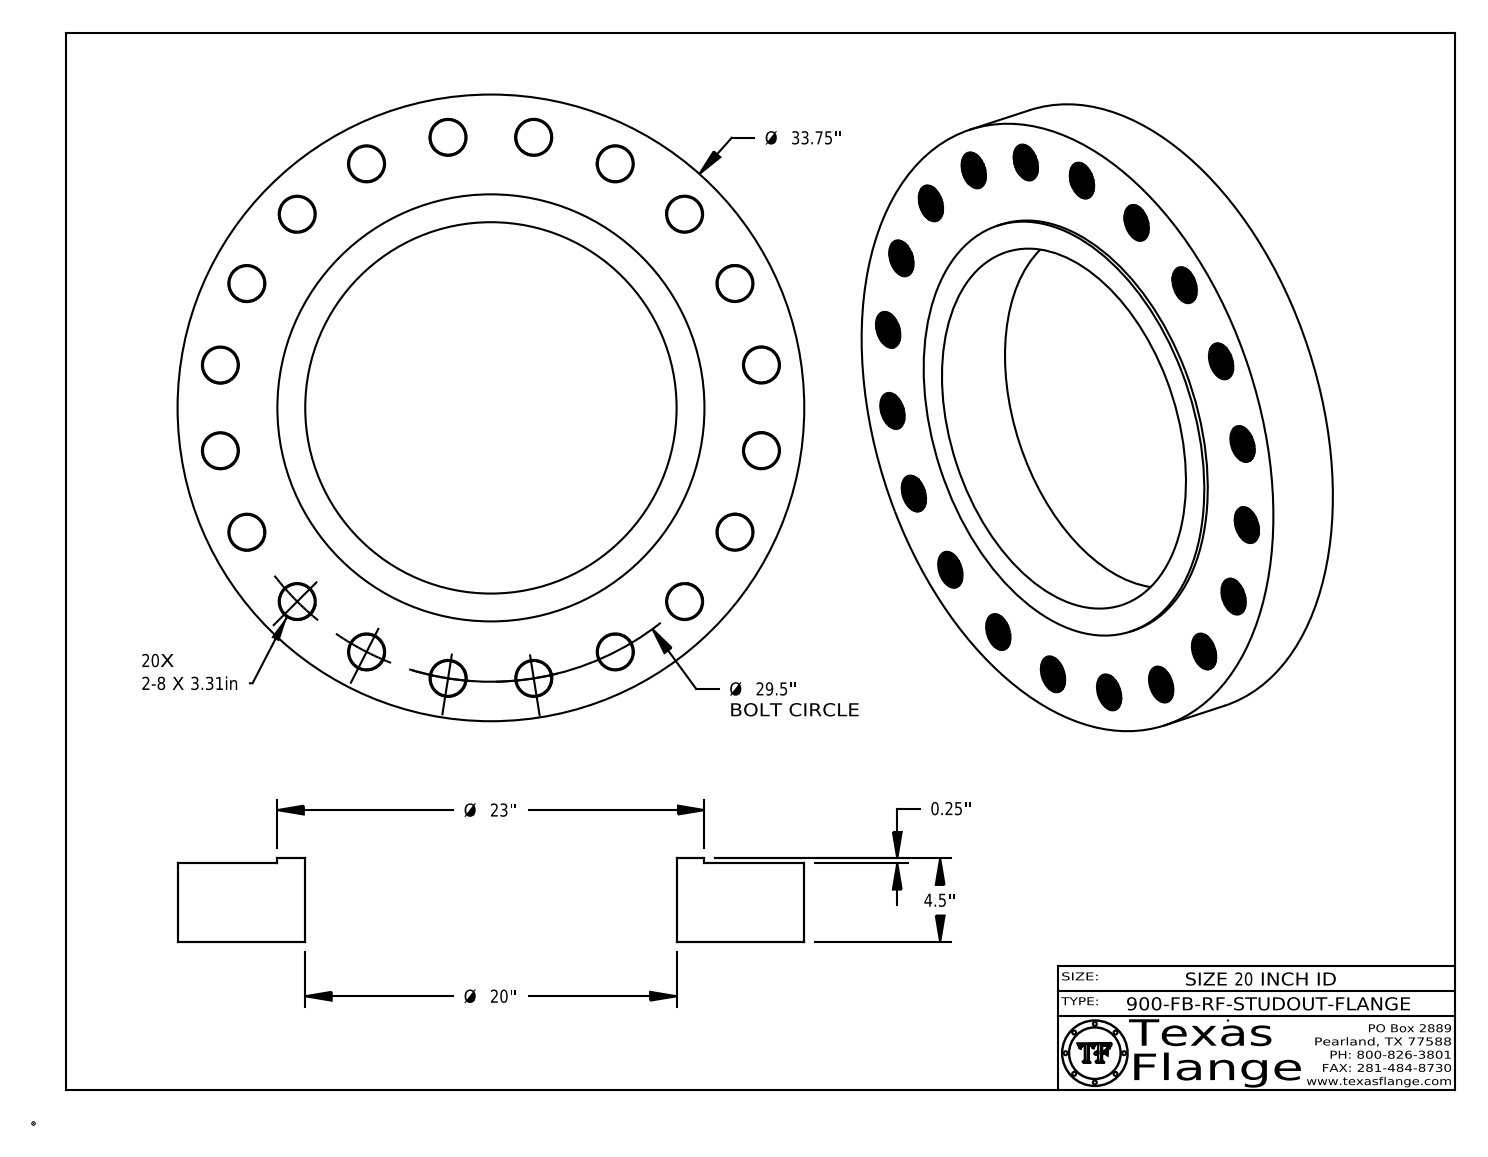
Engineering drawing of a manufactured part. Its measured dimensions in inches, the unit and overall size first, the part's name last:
Units: inches
Overall size (bounding box): 33.75 × 33.75 × 4.5
Round holes (diameter × count): ⌀1.875 ×20, ⌀1 ×1, ⌀20 ×1
Round bosses / shafts (diameter × count): ⌀0.061 ×8, ⌀33.75 ×1, ⌀23 ×1, ⌀0.788 ×1
Main face-to-face distances: 4.25, 0.25, 4.5, 4.485, 4.235, 0.015, 0.298, 0.293, 0.054, 0.248
Hole centre spacings: 4.615, 9.116, 13.393, 17.34, 20.86, 23.866, 26.285, 29.137
Volume: 2 291 in³ · Surface area: 2 424 in²
Bodies: 1 solid, 2714 faces (368 planar, 786 cylindrical, 1560 other)
Part name (STEP PRODUCT): 20-900-FB-RF-STUDOUT-FLANGE
STEP written by: CATIA V5 STEP AP214 (AUTOMOTIVE_DESIGN)
